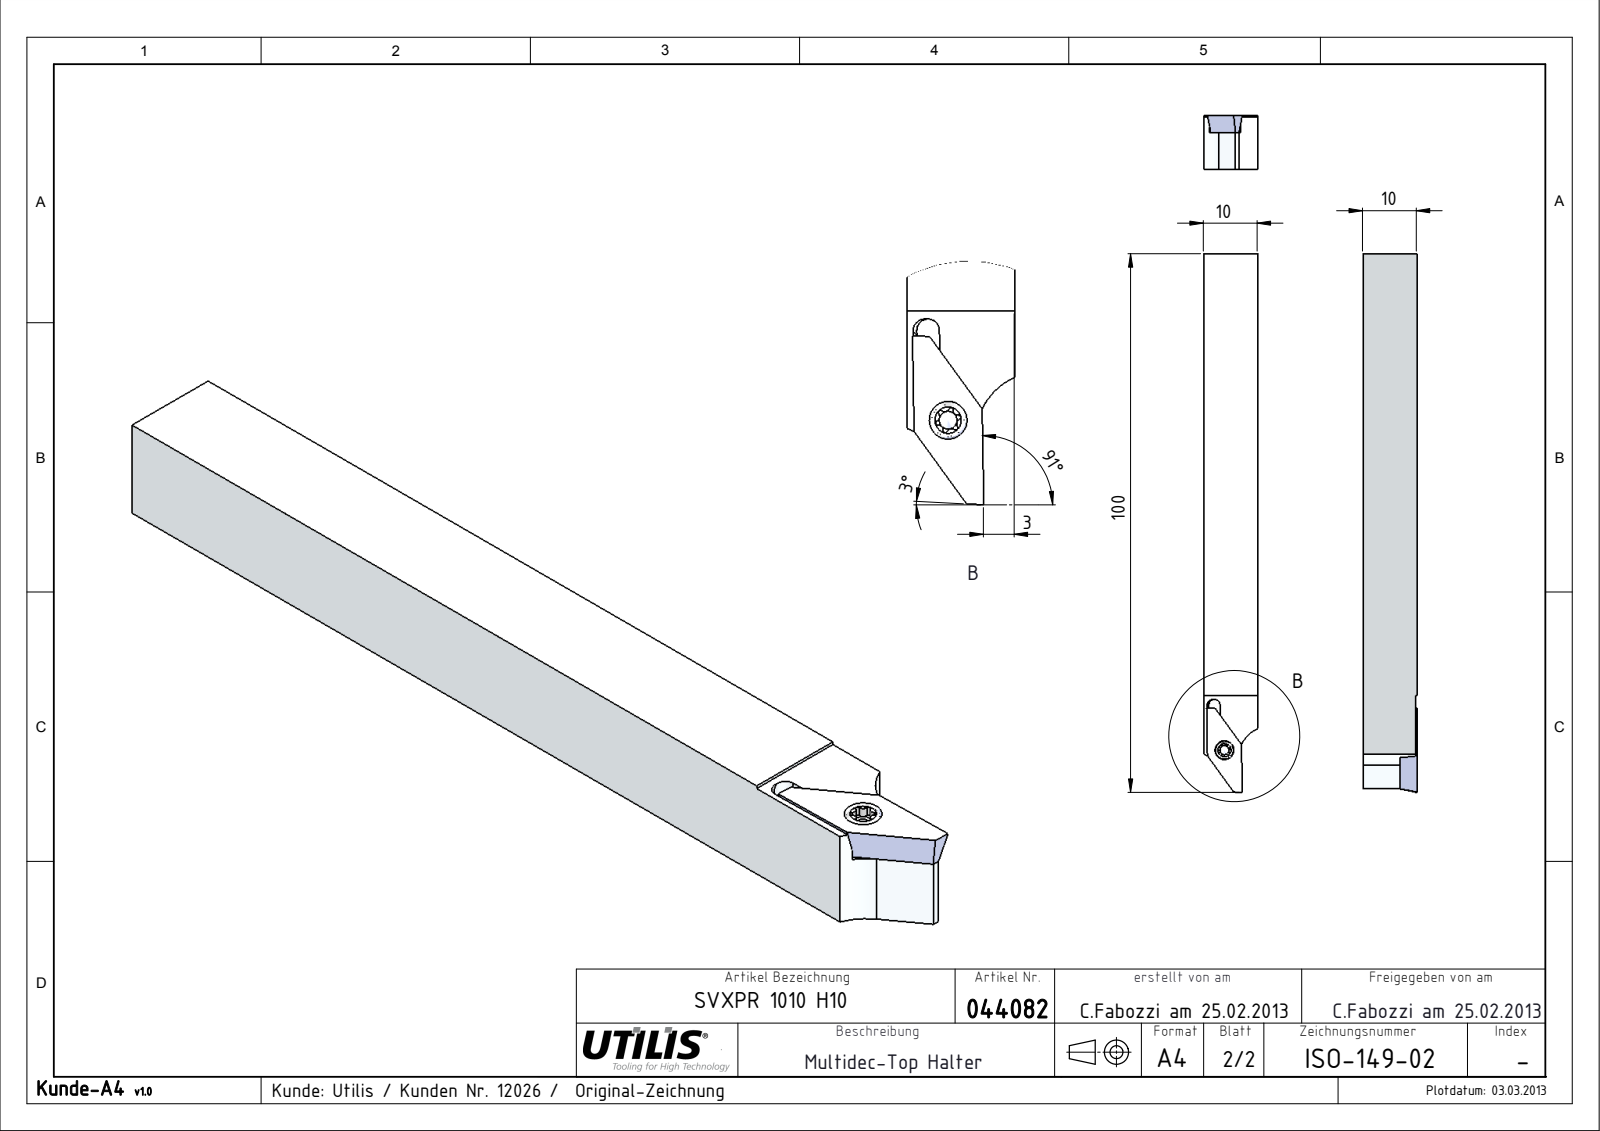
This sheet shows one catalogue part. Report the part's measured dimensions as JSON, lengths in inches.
{"part_name": "VPGT 10 R_VPGT 10 R; MSP-7_M2,5X6-TX8 CERATIZIT Schraube; ISO-149-02; ISO-149-Kunde_02", "step_written_by": "SolidWorks 2015 (CONFIG_CONTROL_DESIGN)", "units": "inches", "bodies": {"solids": 3, "faces": 71, "planar": 27, "cylindrical": 27, "other": 17}, "overall_size": [3.937, 0.394, 0.394], "volume_in3": 0.57, "surface_area_in2": 6.749, "round_holes": [[0.081, 1], [0.118, 1]], "round_bosses_or_shafts": [[0.136, 1], [0.098, 1]], "partial_cylinders_radius": [[0.008, 6], [0.018, 6], [0.236, 2], [0.041, 1]], "face_to_face_distances": [0.394, 0.269, 0.125, 0.382, 0.113, 0.21, 0.083, 0.127, 0.209, 3.228]}
